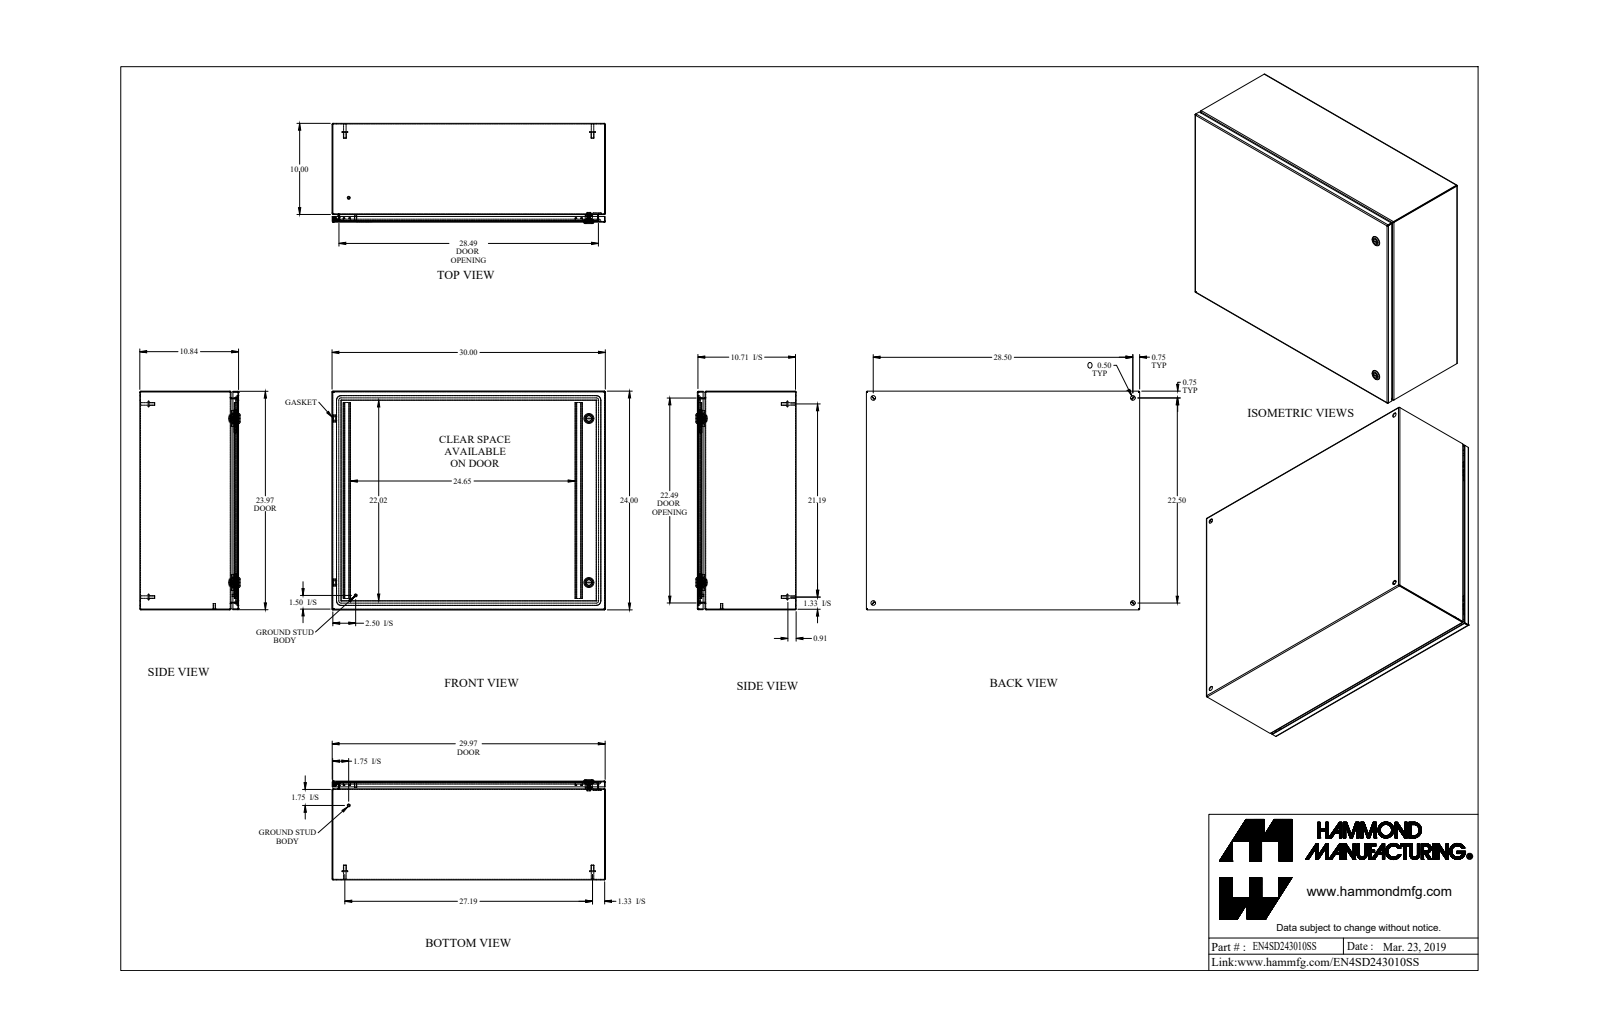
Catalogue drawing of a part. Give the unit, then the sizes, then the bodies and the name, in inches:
Units: inches
Overall size (bounding box): 30 × 24 × 11.002
Round holes (diameter × count): ⌀0.5 ×6, ⌀0.197 ×2, ⌀0.387 ×2, ⌀0.63 ×2, ⌀0.768 ×2, ⌀0.172 ×1, ⌀0.24 ×1, ⌀0.242 ×1
Round bosses / shafts (diameter × count): ⌀0.625 ×6, ⌀0.313 ×6, ⌀0.275 ×4, ⌀1.1 ×2, ⌀0.785 ×2, ⌀0.525 ×2, ⌀0.25 ×2, ⌀0.236 ×2
Partial cylindrical surfaces — rounded edges, fillets, slot ends (radius × count): R0.036 ×16, R0.108 ×16, R0.25 ×16, R0.01 ×12, R0.048 ×12, R0.1 ×8, R0.006 ×4, R0.062 ×4
Main face-to-face distances: 0.072, 10.77, 10.698, 10.842, 23.928, 29.928, 23.856, 24, 29.856, 30
Hole centre spacings: 22.5, 27.531, 28.5, 36.311, 2.488, 2.489, 17.999, 20.277
Volume: 209.8 in³ · Surface area: 5 869 in²
Bodies: 29 solids, 790 faces (387 planar, 263 cylindrical, 140 other)
Part name (STEP PRODUCT): EN4SD243010SS
STEP written by: SolidWorks 2019 (AUTOMOTIVE_DESIGN)
